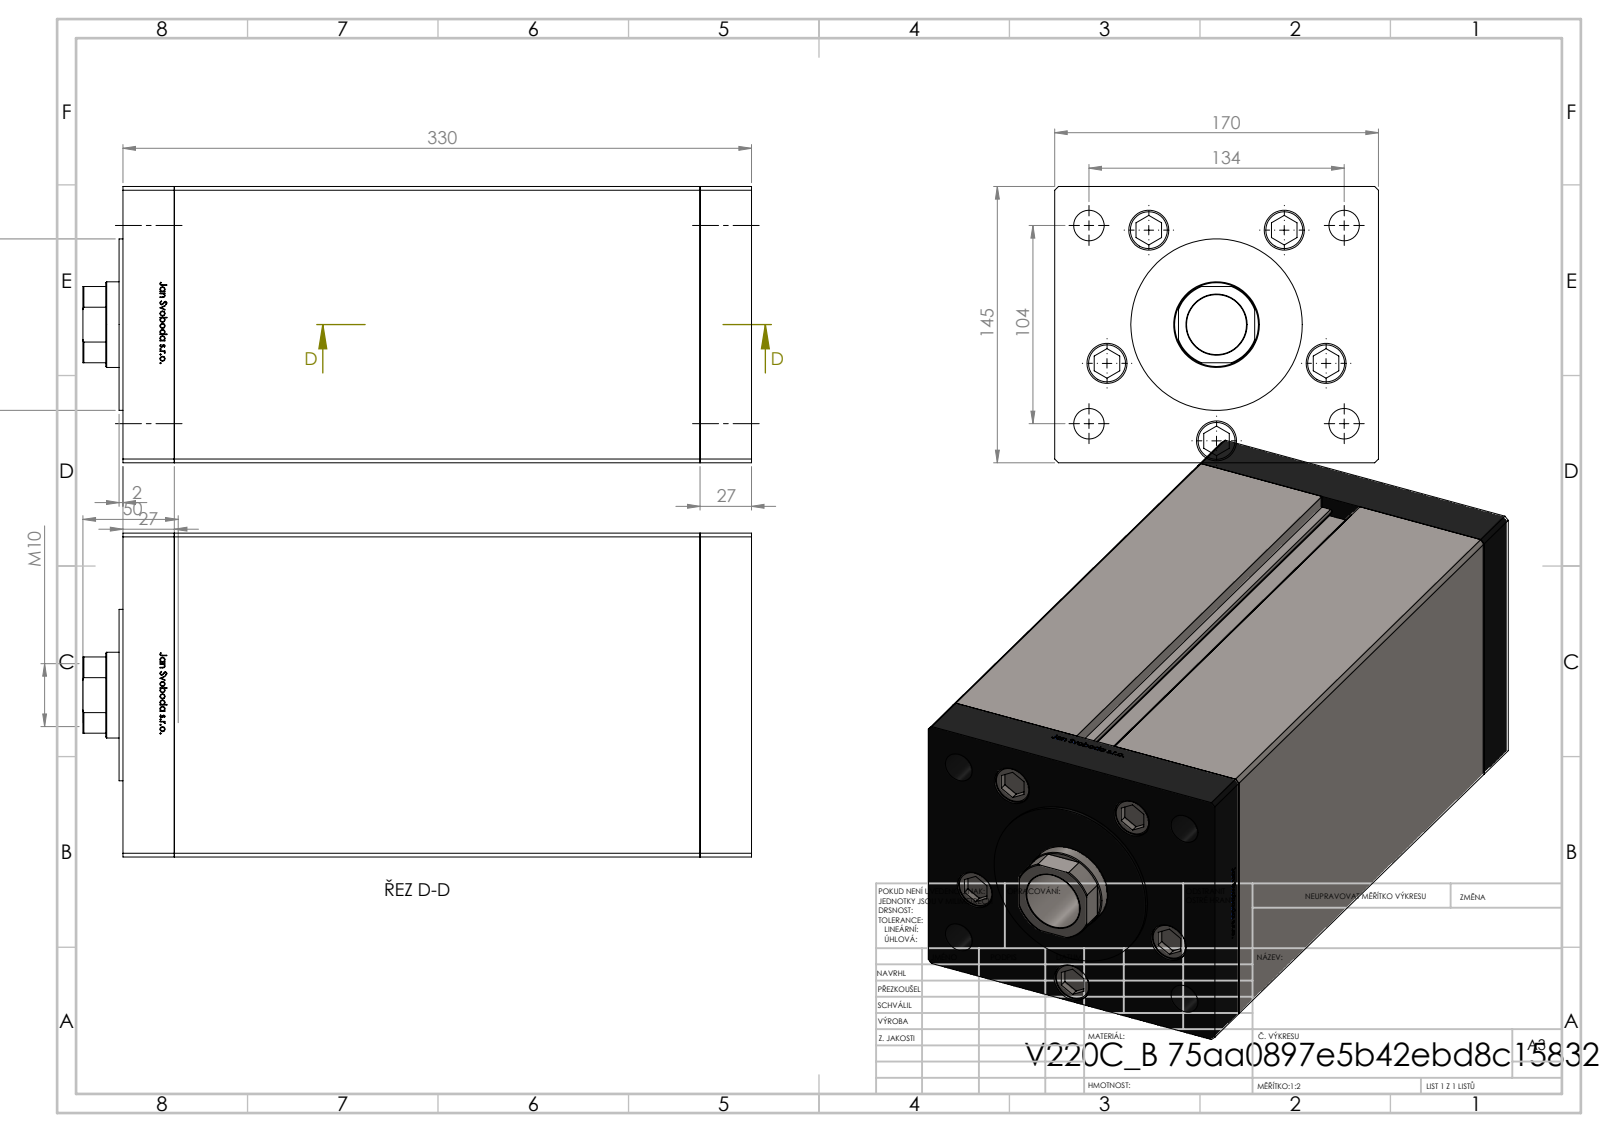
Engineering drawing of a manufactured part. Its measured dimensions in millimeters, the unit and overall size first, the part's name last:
Units: millimetres
Overall size (bounding box): 351 × 170 × 145
Round holes (diameter × count): ⌀17.5 ×5, ⌀21 ×5, ⌀16 ×4, ⌀2 ×2, ⌀13.16 ×2, ⌀31.5 ×1, ⌀45 ×1
Round bosses / shafts (diameter × count): ⌀8 ×5, ⌀100 ×1, ⌀90 ×1
Partial cylindrical surfaces — rounded edges, fillets, slot ends (radius × count): R0.93 ×2, R22 ×1
Main face-to-face distances: 145, 170, 27, 303, 276, 38, 11, 330, 265, 292
Hole centre spacings: 61, 84.81, 31.53, 33.06, 67.6, 70.44, 72.95, 73.26
Volume: 6 697 000 mm³ · Surface area: 565 757 mm²
Bodies: 14 solids, 1185 faces (464 planar, 147 cylindrical, 574 other)
Part name (STEP PRODUCT): V220C BACK_B; ALLEN BOLT; V220C_VC_B; V220C_FRONT_B (+1 more)
STEP written by: SolidWorks 2019 (CONFIG_CONTROL_DESIGN)
